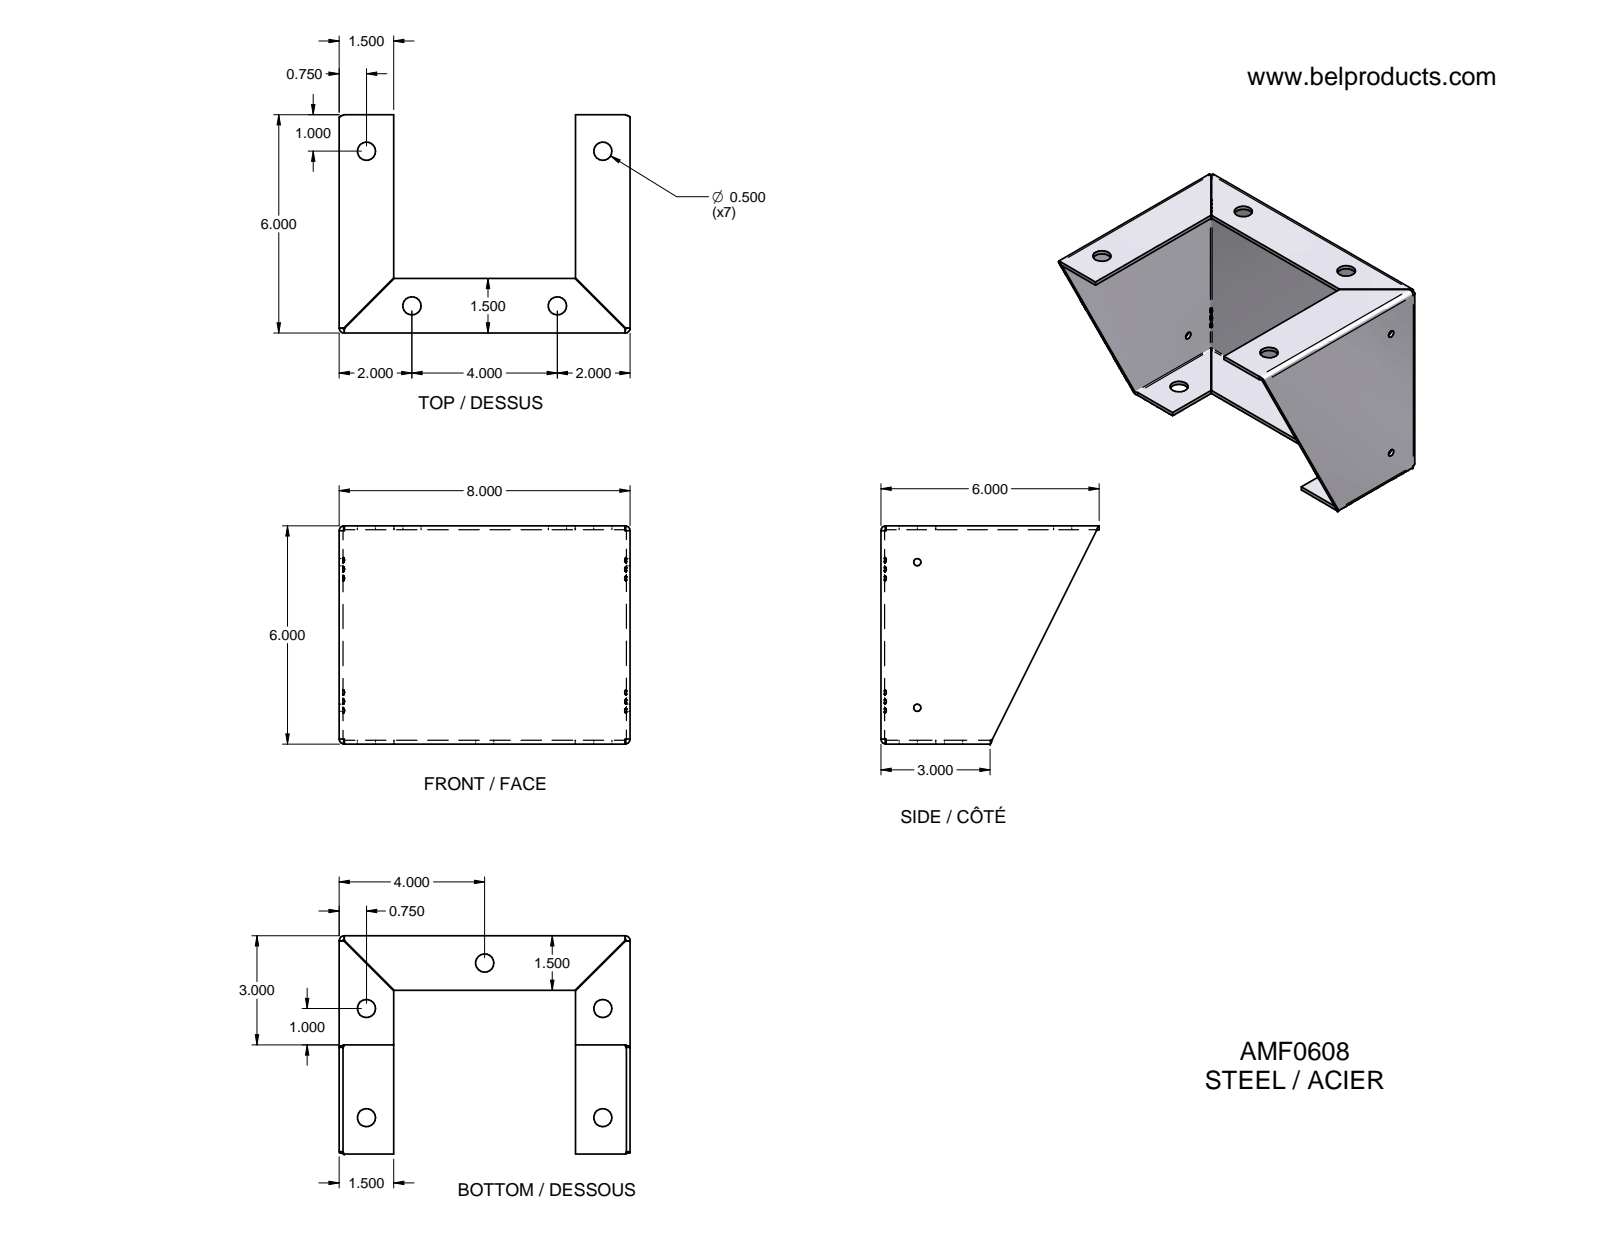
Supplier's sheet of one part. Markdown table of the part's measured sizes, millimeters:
| quantity | value |
| --- | --- |
| STEP written by | Unknown (AUTOMOTIVE_DESIGN) |
| units | millimeters |
| bodies | 1 solid, 281 faces (90 planar, 123 cylindrical, 68 other) |
| overall size | 203.2 × 152.4 × 152.4 |
| volume | 233 752 mm³ |
| surface area | 180 164 mm² |
| round holes (diameter × count) | 12.7 × 7, 5.11 × 2 |
| partial cylindrical surfaces (radius × count) | 1.51 × 18, 1.59 × 18, 0.81 × 8, 3.48 × 8, 1.01 × 2 |
| main face-to-face distances | 2.67, 200.53, 149.73, 203.2, 197.86, 152.4, 147.06, 38.1, 35.43, 165.1 |
| hole center spacings | 44.9, 50.8, 76.2, 88.45, 101.6, 112.52, 135.9, 137.08 |
